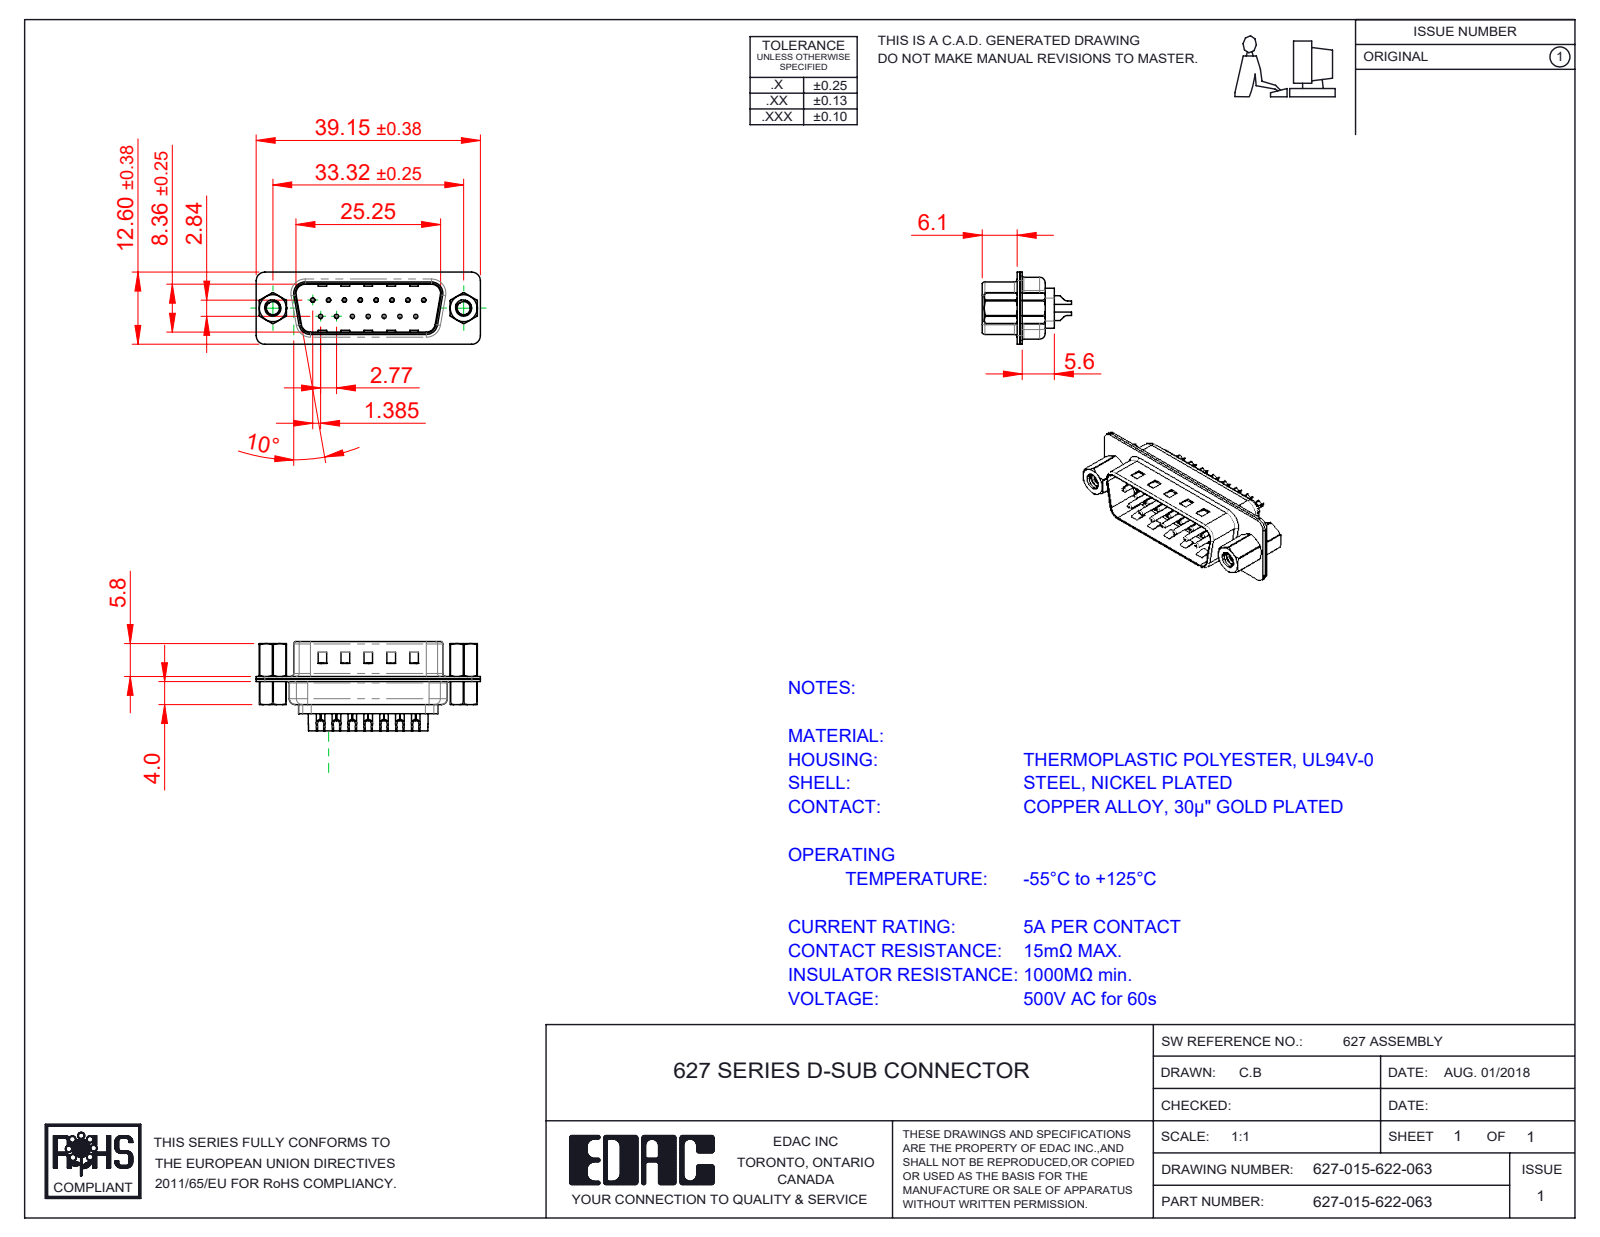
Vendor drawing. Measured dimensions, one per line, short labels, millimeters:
name: 627 Housing_15 LP; 627 Contact Row 1_22L; 627 Contact Row 2_22L; 627 4-40 Threaded Rivet (+4 more)
written by: SolidWorks 2020 (CONFIG_CONTROL_DESIGN)
unit: mm
bodies: 22 solids, 1422 faces (371 planar, 638 cylindrical, 413 other)
size: 39.15 × 15.35 × 12.6
volume: 2 043 mm³; area: 5 895 mm²
holes: 15× ⌀0.35, 15× ⌀1.1, 15× ⌀1.6, 2× ⌀2.26, 2× ⌀2.29, 2× ⌀4, 2× ⌀4.8
bosses: 15× ⌀2, 15× ⌀1.5, 15× ⌀0.75, 2× ⌀5, 2× ⌀4.9, 2× ⌀2.79
rounds: 16× R1.5, 12× R2, 8× R0.5, 8× R1.6, 6× R1, 4× R0.25, 4× R0.6, 4× R0.65
face distances: 0.4, 0.45, 0.9, 0.82, 9.58, 8.76, 1.5, 1.4, 6.5, 5.6
hole spacings: 3.16, 2.77, 5.54, 8.31, 11.08, 5.03, 5.04, 7.48
